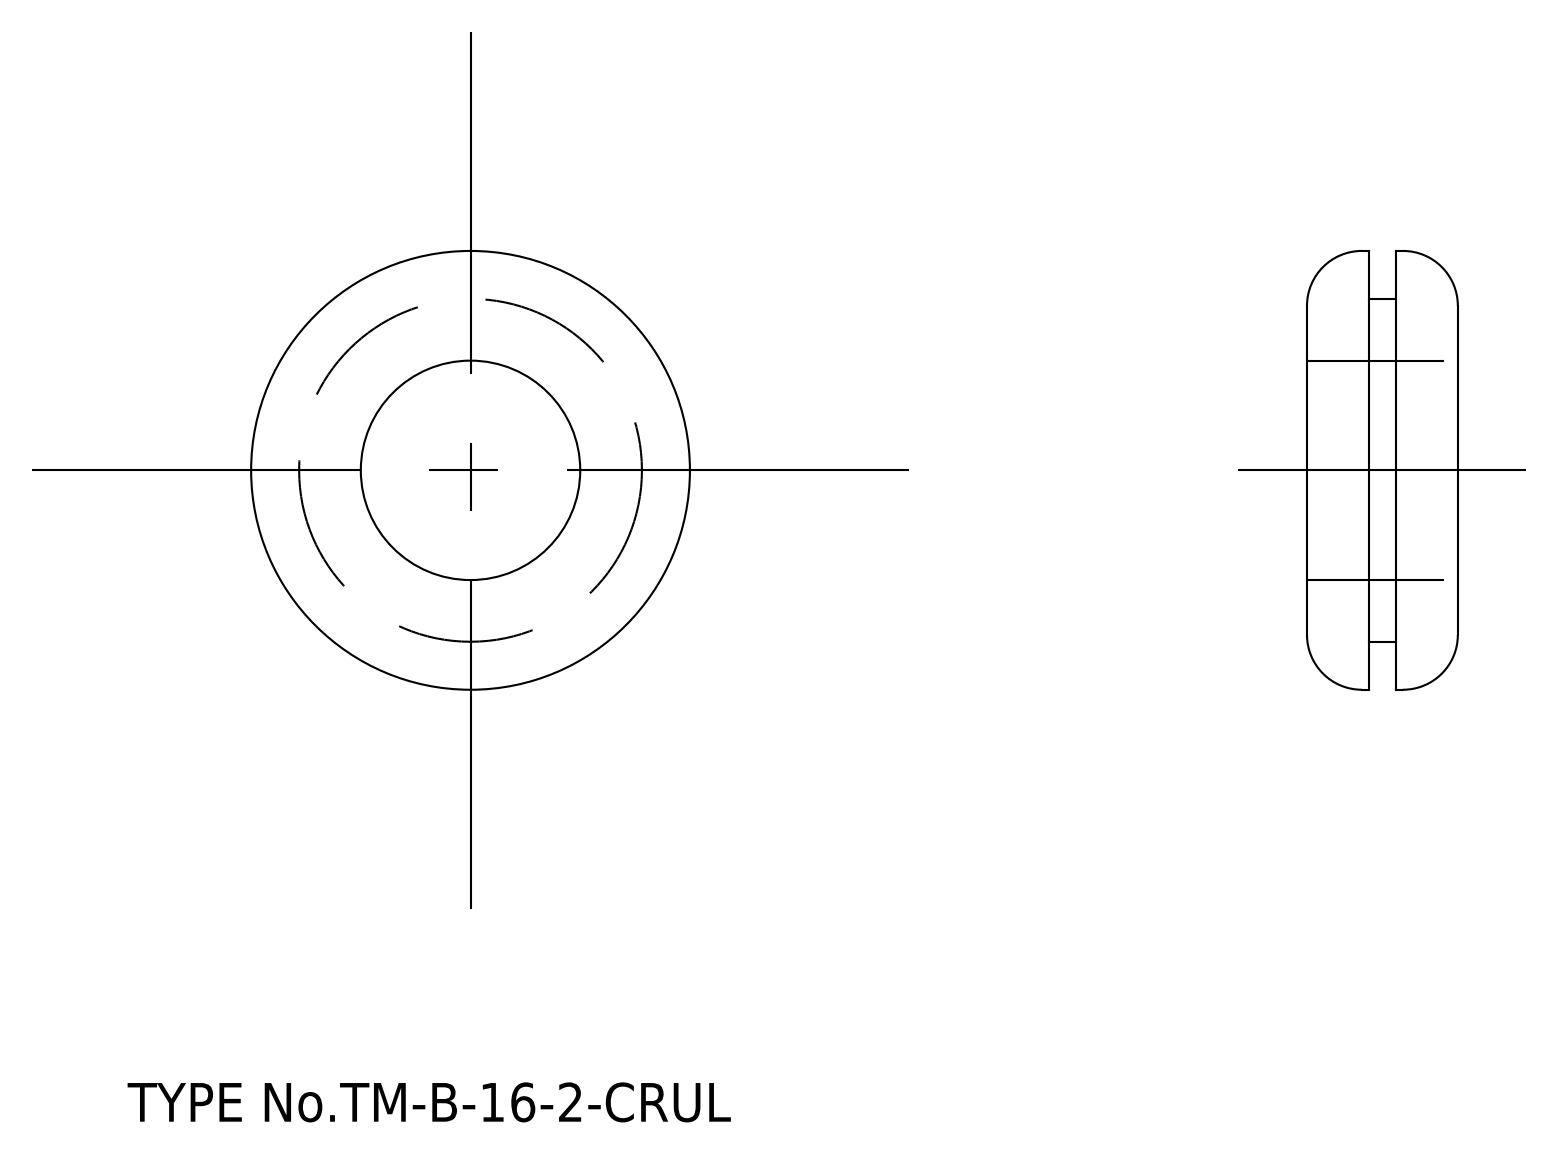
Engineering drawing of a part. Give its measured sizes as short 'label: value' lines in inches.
written by: spGate 15.6.1 (AUTOMOTIVE_DESIGN)
unit: in
bodies: 1 solid, 16 faces (4 planar, 8 cylindrical, 4 other)
size: 1.26 × 1.26 × 0.433
volume: 0.327 in³; area: 4.79 in²
holes: 1× ⌀0.63
bosses: 1× ⌀1.26, 1× ⌀0.984
face distances: 0.177, 0.256, 0.079, 0.433
